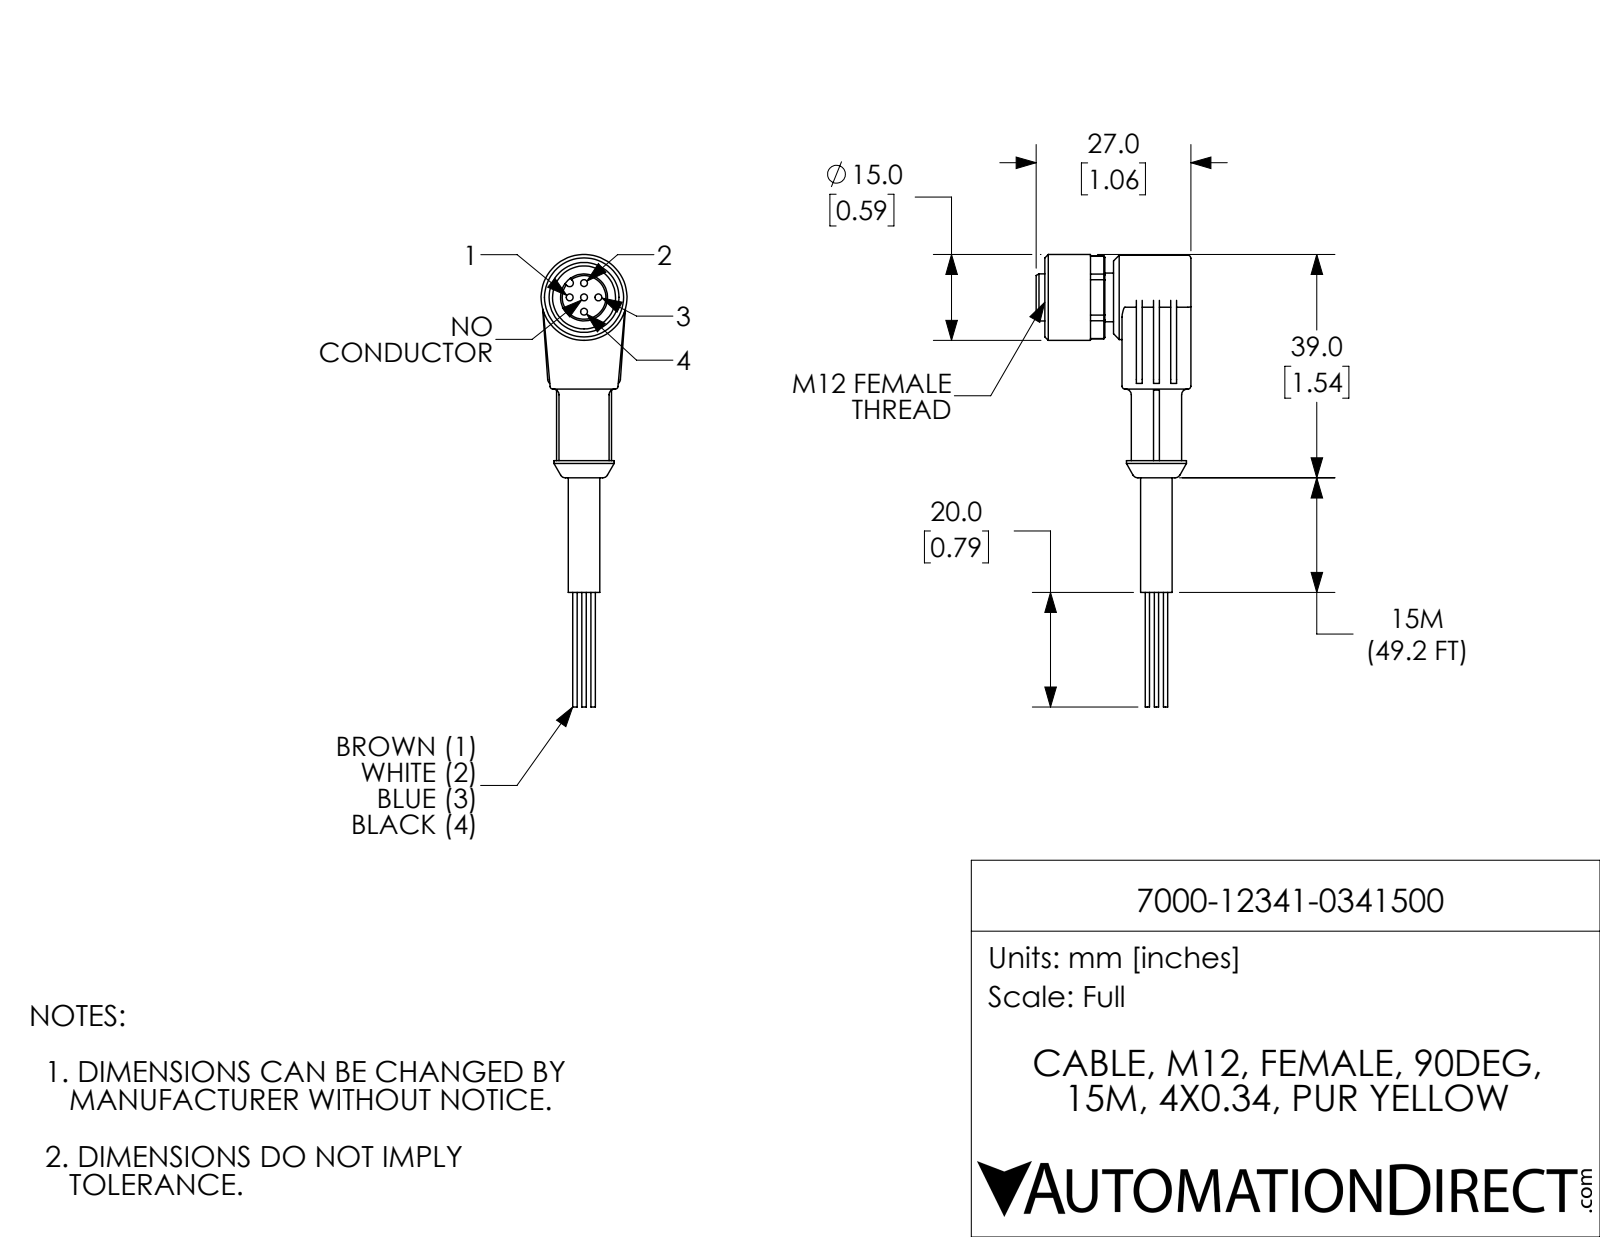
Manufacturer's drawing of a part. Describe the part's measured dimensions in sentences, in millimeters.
The part is named "7000-12341-0341500". Its 3-D file was written by "SolidWorks 2021 (CONFIG_CONTROL_DESIGN)". It is 1 solid with 152 faces: 65 planar, 59 cylindrical and 28 other. Overall it measures 79 by 27 by 15 millimeters. Its volume is 6 830 cubic millimeters and its surface area 3 804 square millimeters. Round holes: 5 of diameter 1.2, 1 of diameter 4.8, 1 of diameter 11. Round bosses or shafts: 4 of diameter 0.8, 1 of diameter 15, 1 of diameter 14.7, 1 of diameter 10.5, 1 of diameter 8.8, 1 of diameter 8.5, 1 of diameter 8.2, 1 of diameter 5.5. Partial cylindrical surfaces (rounded edges, fillets, slot ends): 8 of radius 0.5, 2 of radius 1, 1 of radius 0.7, 1 of radius 7.2. The main face-to-face distances are 12, 1.5, 3, 13.5, 15, 5.5, 9.5, 6, 8, 12.5. The hole center spacings are 2.5, 3.5, 5.
